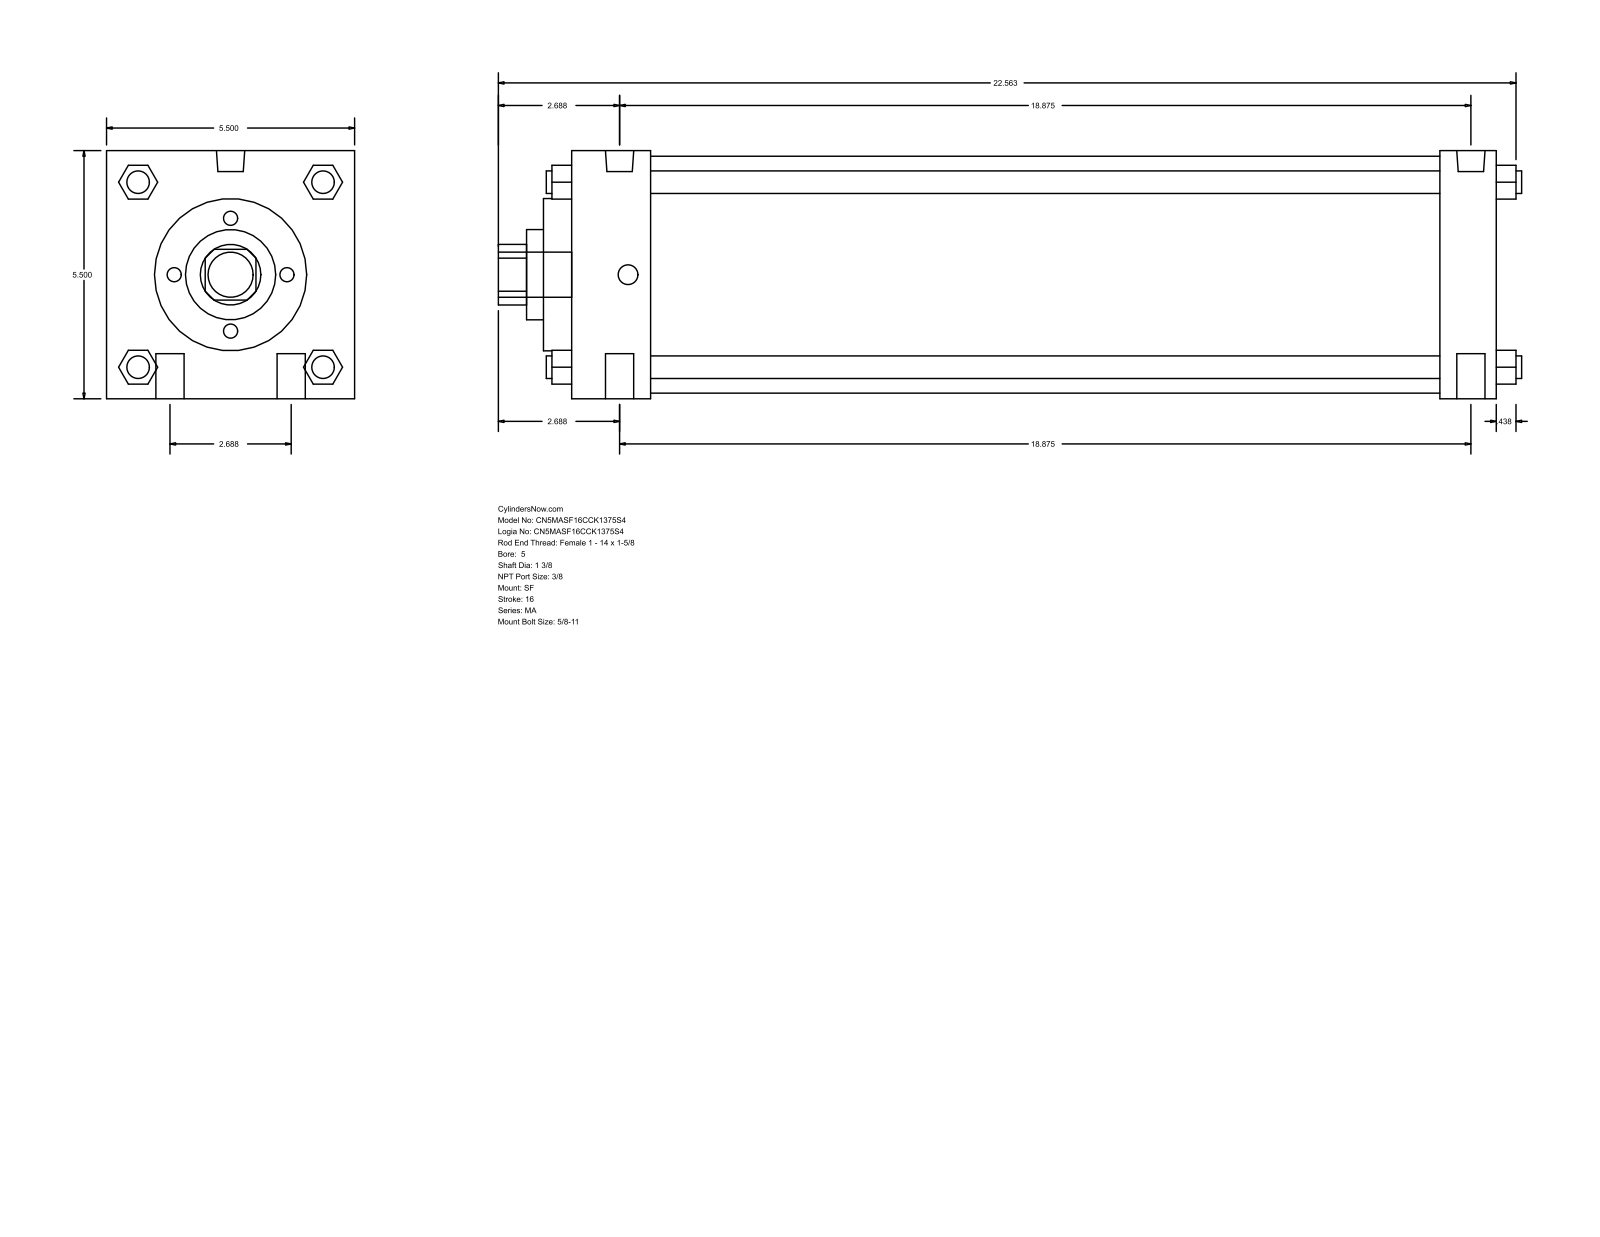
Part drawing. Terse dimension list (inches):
name: MA_SF__0500_1.375
written by: GSSL Pune (CONFIG_CONTROL_DESIGN)
unit: in
bodies: 0 solids, 126 faces (95 planar, 31 cylindrical, 0 other)
size: 22.687 × 5.5 × 5.5
holes: 1× ⌀1.375, 1× ⌀2, 1× ⌀3.375, 1× ⌀5.25
bosses: 4× ⌀0.625, 4× ⌀0.5, 2× ⌀0.627, 2× ⌀0.437, 1× ⌀1
rounds: 1× R0.672
face distances: 5.5, 20.5, 1.75, 19.25, 17.5, 18.75, 1.25, 0.625, 2.375, 19.875
